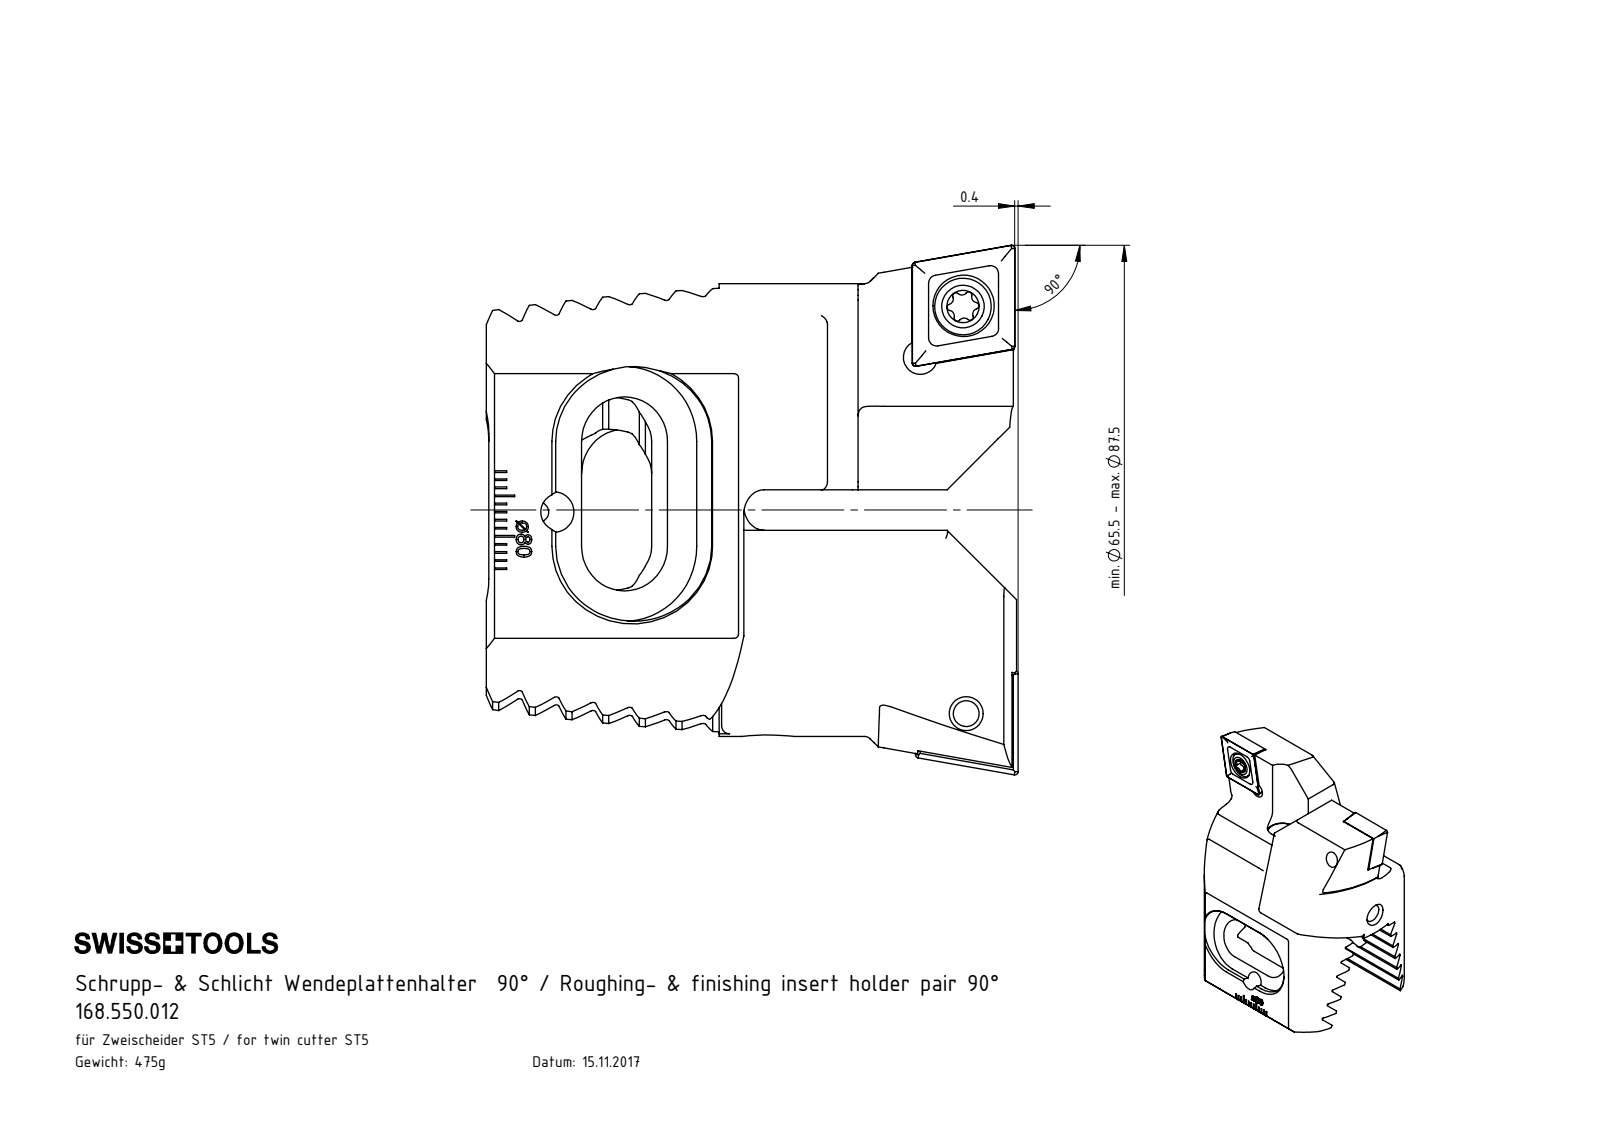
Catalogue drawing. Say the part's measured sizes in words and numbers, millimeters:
The part is named "ZC5-xxx.001.037_A_versetzt Combi; ISO 4028 - M3 x 5_M3x8; WCC-ER2.001.010_A; Z55-ER3.001.020 (+3 more)". Its 3-D file was written by "SolidWorks 2017 (CONFIG_CONTROL_DESIGN)". It is 8 solids with 706 faces: 349 planar, 137 cylindrical and 220 other. Overall it measures 65.8 by 65.5 by 44.2 millimeters. Its volume is 60 917 cubic millimeters and its surface area 22 421 square millimeters. Round holes: 4 of diameter 4.2, 2 of diameter 5, 2 of diameter 5.5, 2 of diameter 7.6, 1 of diameter 2, 1 of diameter 2.5, 1 of diameter 8. Round bosses or shafts: 2 of diameter 7, 2 of diameter 5, 1 of diameter 6, 1 of diameter 4, 1 of diameter 3, 1 of diameter 2. Partial cylindrical surfaces (rounded edges, fillets, slot ends): 14 of radius 1, 12 of radius 0.34, 12 of radius 0.39, 6 of radius 0.69, 6 of radius 0.69, 4 of radius 3, 4 of radius 5.5, 4 of radius 9.25. The main face-to-face distances are 4.07, 8.14, 12.21, 16.28, 20.35, 7.85, 1.69, 17.34, 26.86, 44.2. The hole center spacings are 44.41, 44.51, 50.43, 8.08, 8.2, 8.21, 8.33, 16.
